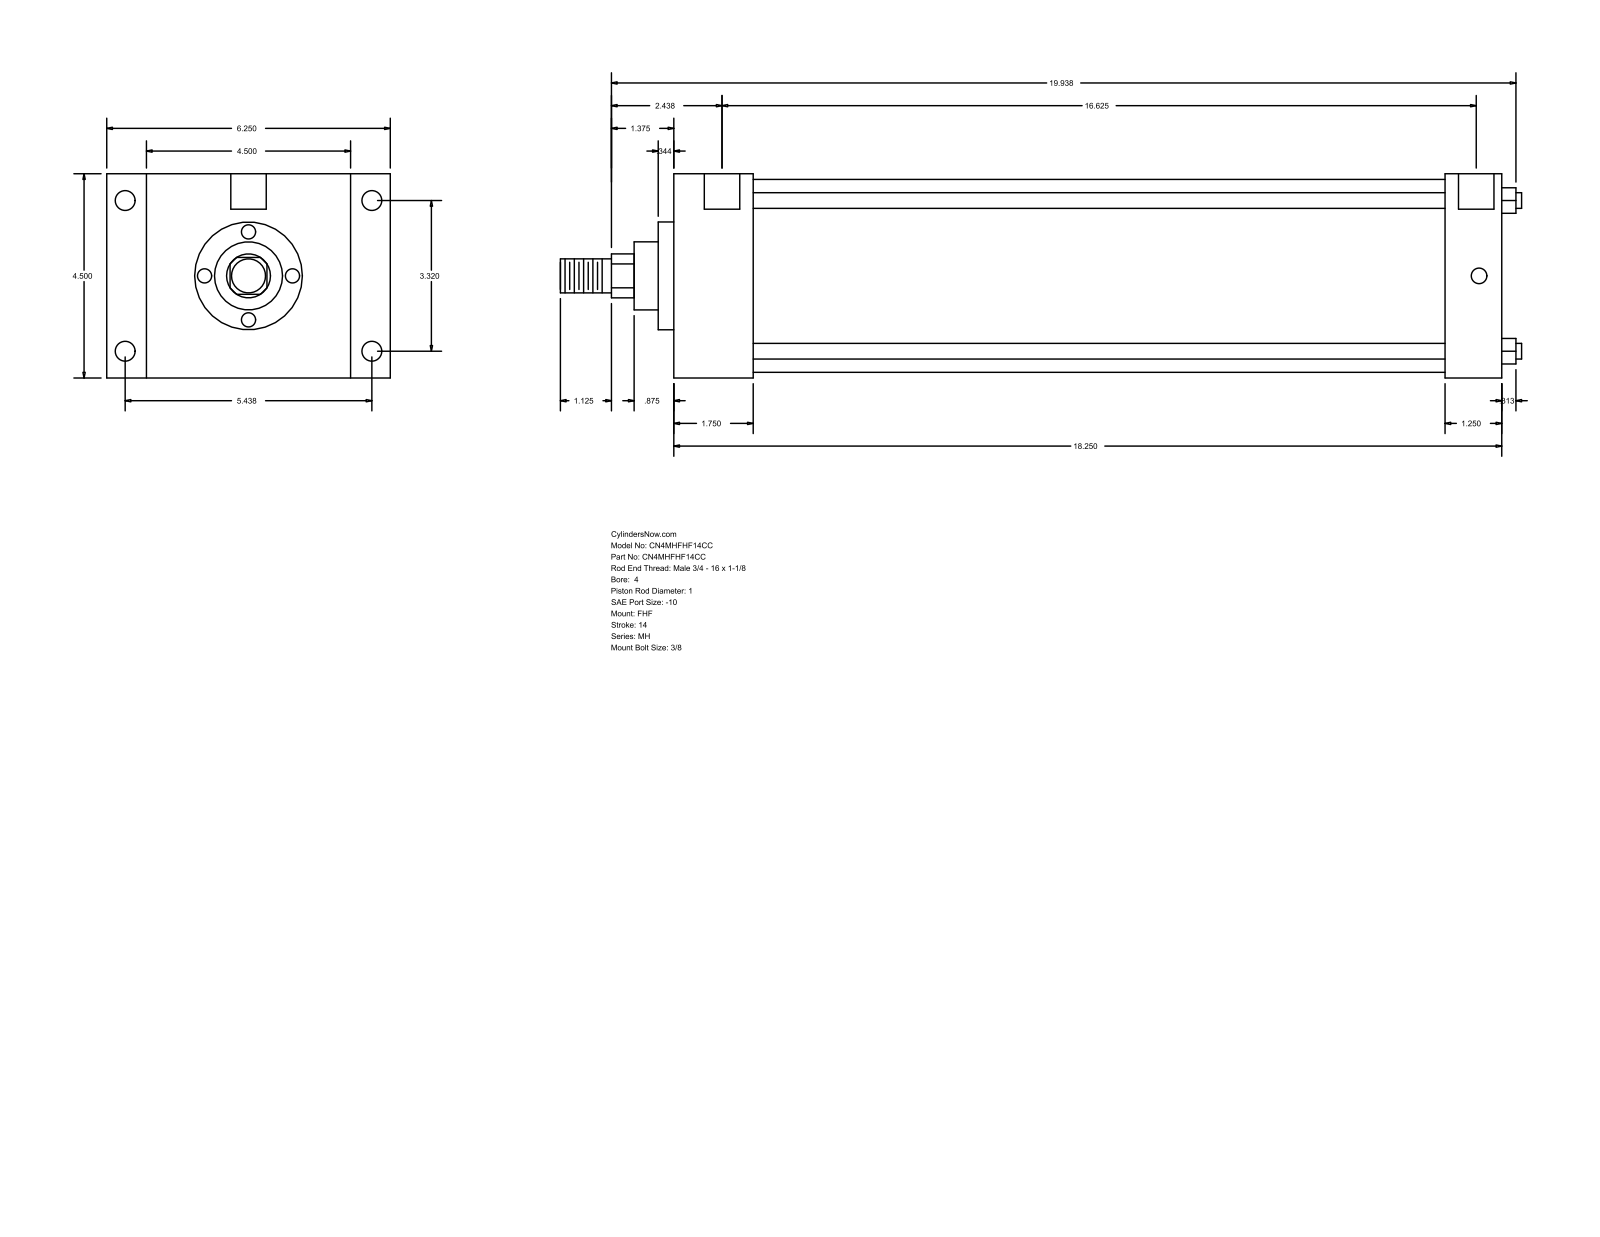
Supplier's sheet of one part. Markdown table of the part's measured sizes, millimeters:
| quantity | value |
| --- | --- |
| part name | MH_FHF__0400_1 |
| STEP written by | GSSL Pune (CONFIG_CONTROL_DESIGN) |
| units | millimeters |
| bodies | 0 solids, 90 faces (61 planar, 29 cylindrical, 0 other) |
| overall size | 538.16 × 158.75 × 114.3 |
| round holes (diameter × count) | 8.73 × 4, 11.13 × 4, 19.84 × 2 |
| round bosses / shafts (diameter × count) | 8.76 × 4, 107.95 × 1, 60.33 × 1, 38.1 × 1, 25.4 × 1, 19.05 × 1 |
| partial cylindrical surfaces (radius × count) | 12.29 × 1 |
| main face-to-face distances | 114.3, 463.56, 44.46, 419.1, 22.23, 136.53, 158.76, 431.81, 387.35, 31.75 |
| hole center spacings | 1.58, 84.32, 138.12, 161.82, 423.86, 425.44, 422.28 |
